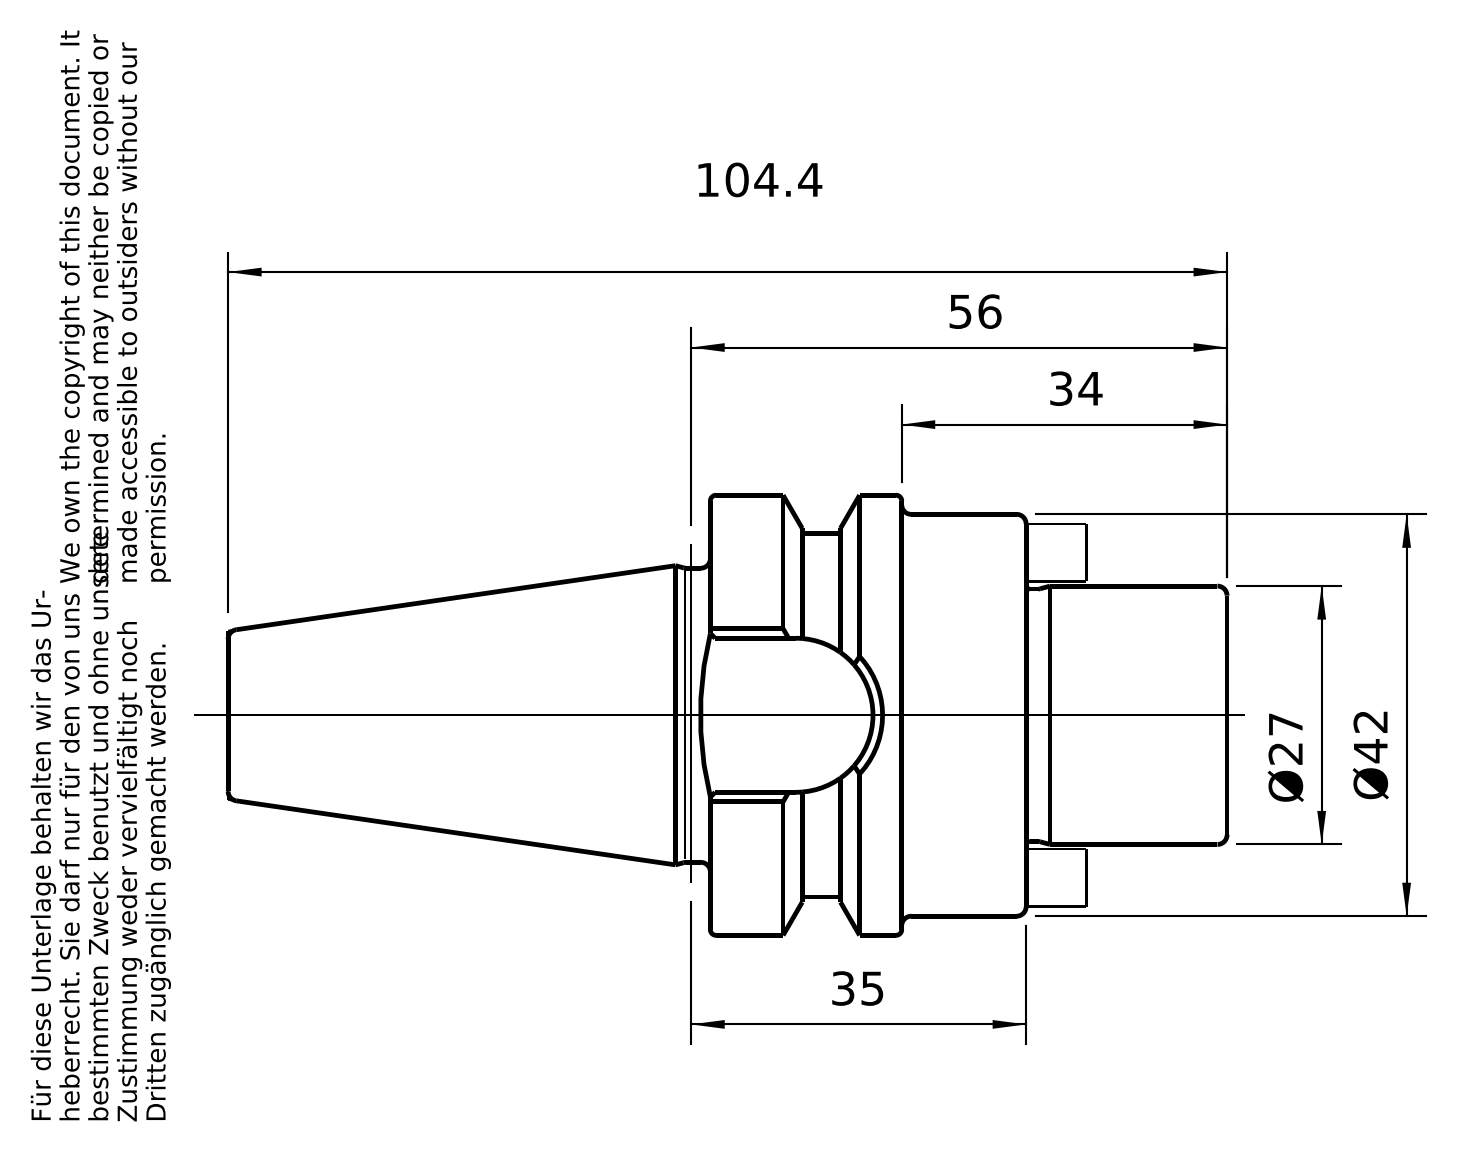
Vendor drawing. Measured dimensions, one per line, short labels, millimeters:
name: 30-550-27
written by: PRO/ENGINEER BY PARAMETRIC TECHNOLOGY CORPORATION, 2010430 (CONFIG_CONTROL_DESIGN)
unit: mm
bodies: 1 solid, 117 faces (41 planar, 26 cylindrical, 50 other)
size: 104.4 × 45.98 × 45.98
volume: 77 604 mm³; area: 17 798 mm²
holes: 1× ⌀10.11, 1× ⌀10.2, 1× ⌀12, 1× ⌀12.51, 1× ⌀13
bosses: 1× ⌀45.98, 1× ⌀42, 1× ⌀30.75, 1× ⌀27, 1× ⌀12.01
rounds: 1× R8.1, 1× R18.88
face distances: 33, 54, 21, 32.3, 34, 3.85, 6, 36.15, 2.15, 30.15
